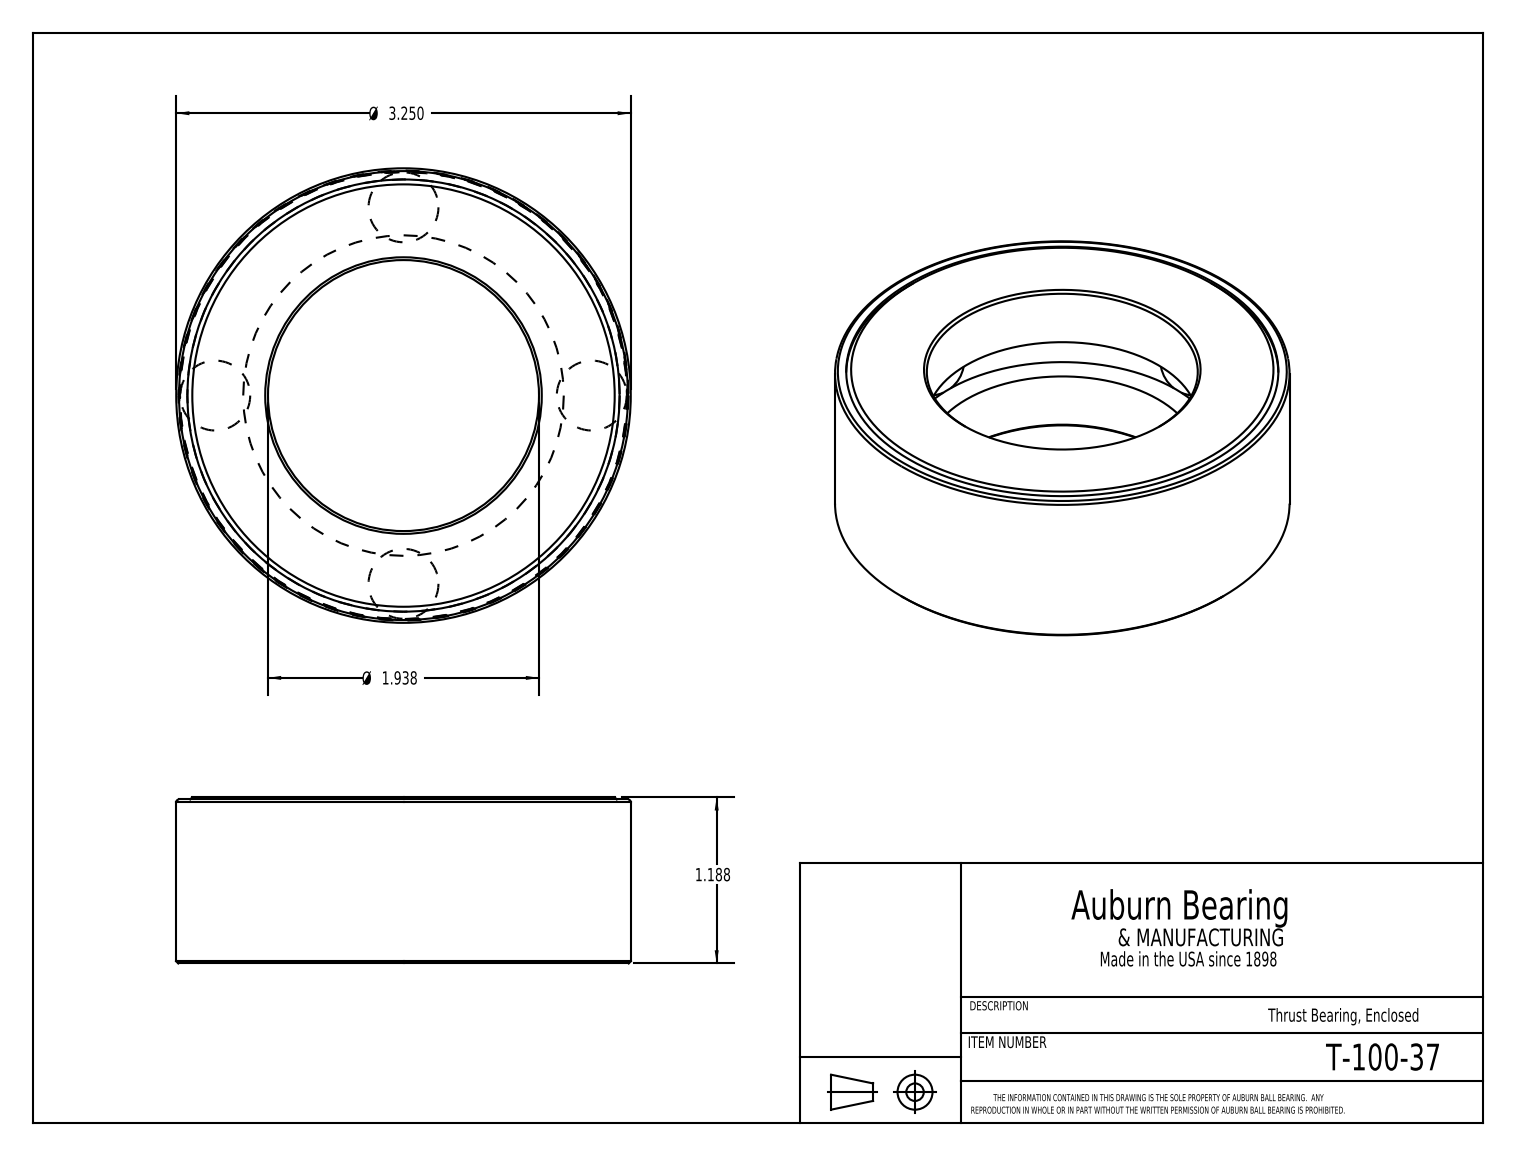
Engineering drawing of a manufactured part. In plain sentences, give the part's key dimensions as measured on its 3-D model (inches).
The part is named "T-100-37". Its 3-D file was written by "SolidWorks 2016 (CONFIG_CONTROL_DESIGN)". It is 6 solids with 28 faces: 9 planar, 7 cylindrical and 12 other. Overall it measures 3.25 by 3.25 by 1.188 inches. Its volume is 4.531 cubic inches and its surface area 54.64 square inches. Round holes: 1 of diameter 1.937, 1 of diameter 3.09, 1 of diameter 3.21. Round bosses or shafts: 1 of diameter 3.25, 1 of diameter 3.196. The main face-to-face distances are 1.187, 0.444, 0.744, 0.3, 1.172, 0.729, 0.429, 0.015, 1.152, 0.709.
